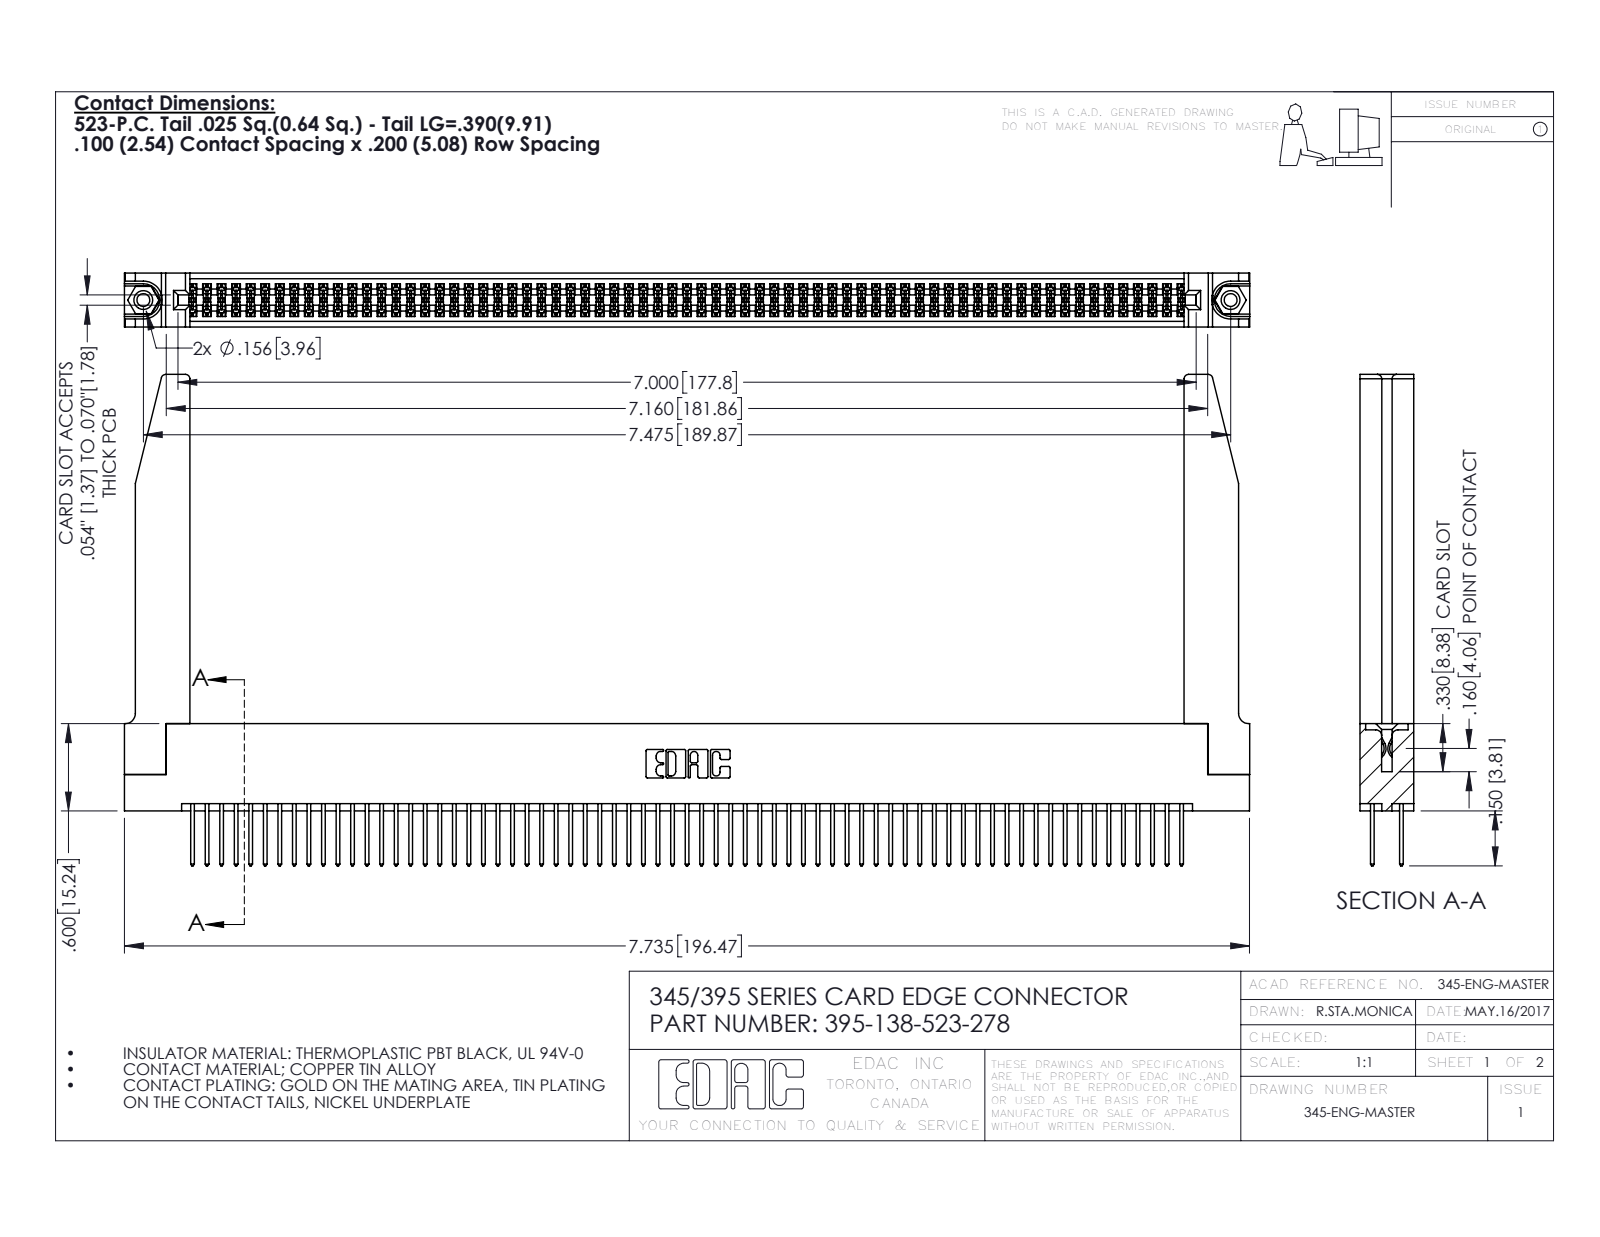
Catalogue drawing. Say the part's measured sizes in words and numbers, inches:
The part is named "345-292-001_345-293-123; 345-220-078_345-220-078; 345 Part_Flush Mounting Lugs - 0.156 Dia-TH; 345-250-001_345-250-001-102 (+1 more)". Its 3-D file was written by "SolidWorks 2016 (CONFIG_CONTROL_DESIGN)". It is 143 solids with 7260 faces: 4776 planar, 2432 cylindrical and 52 other. Overall it measures 7.736 by 3.377 by 0.37 inches. Its volume is 1.672 cubic inches and its surface area 58.33 square inches. Round holes: 2 of diameter 0.089, 2 of diameter 0.125, 2 of diameter 0.156, 1 of diameter 0.064. Round bosses or shafts: 2 of diameter 0.155. Partial cylindrical surfaces (rounded edges, fillets, slot ends): 207 of radius 0.006, 138 of radius 0.01, 22 of radius 0.01, 8 of radius 0.03, 6 of radius 0.007, 6 of radius 0.031, 3 of radius 0.026, 2 of radius 0.014. The main face-to-face distances are 0.072, 0.298, 0.37, 0.2, 0.098, 0.272, 0.025, 0.225, 0.175, 0.149. The hole center spacings are 0.27, 7.239, 7.475.
